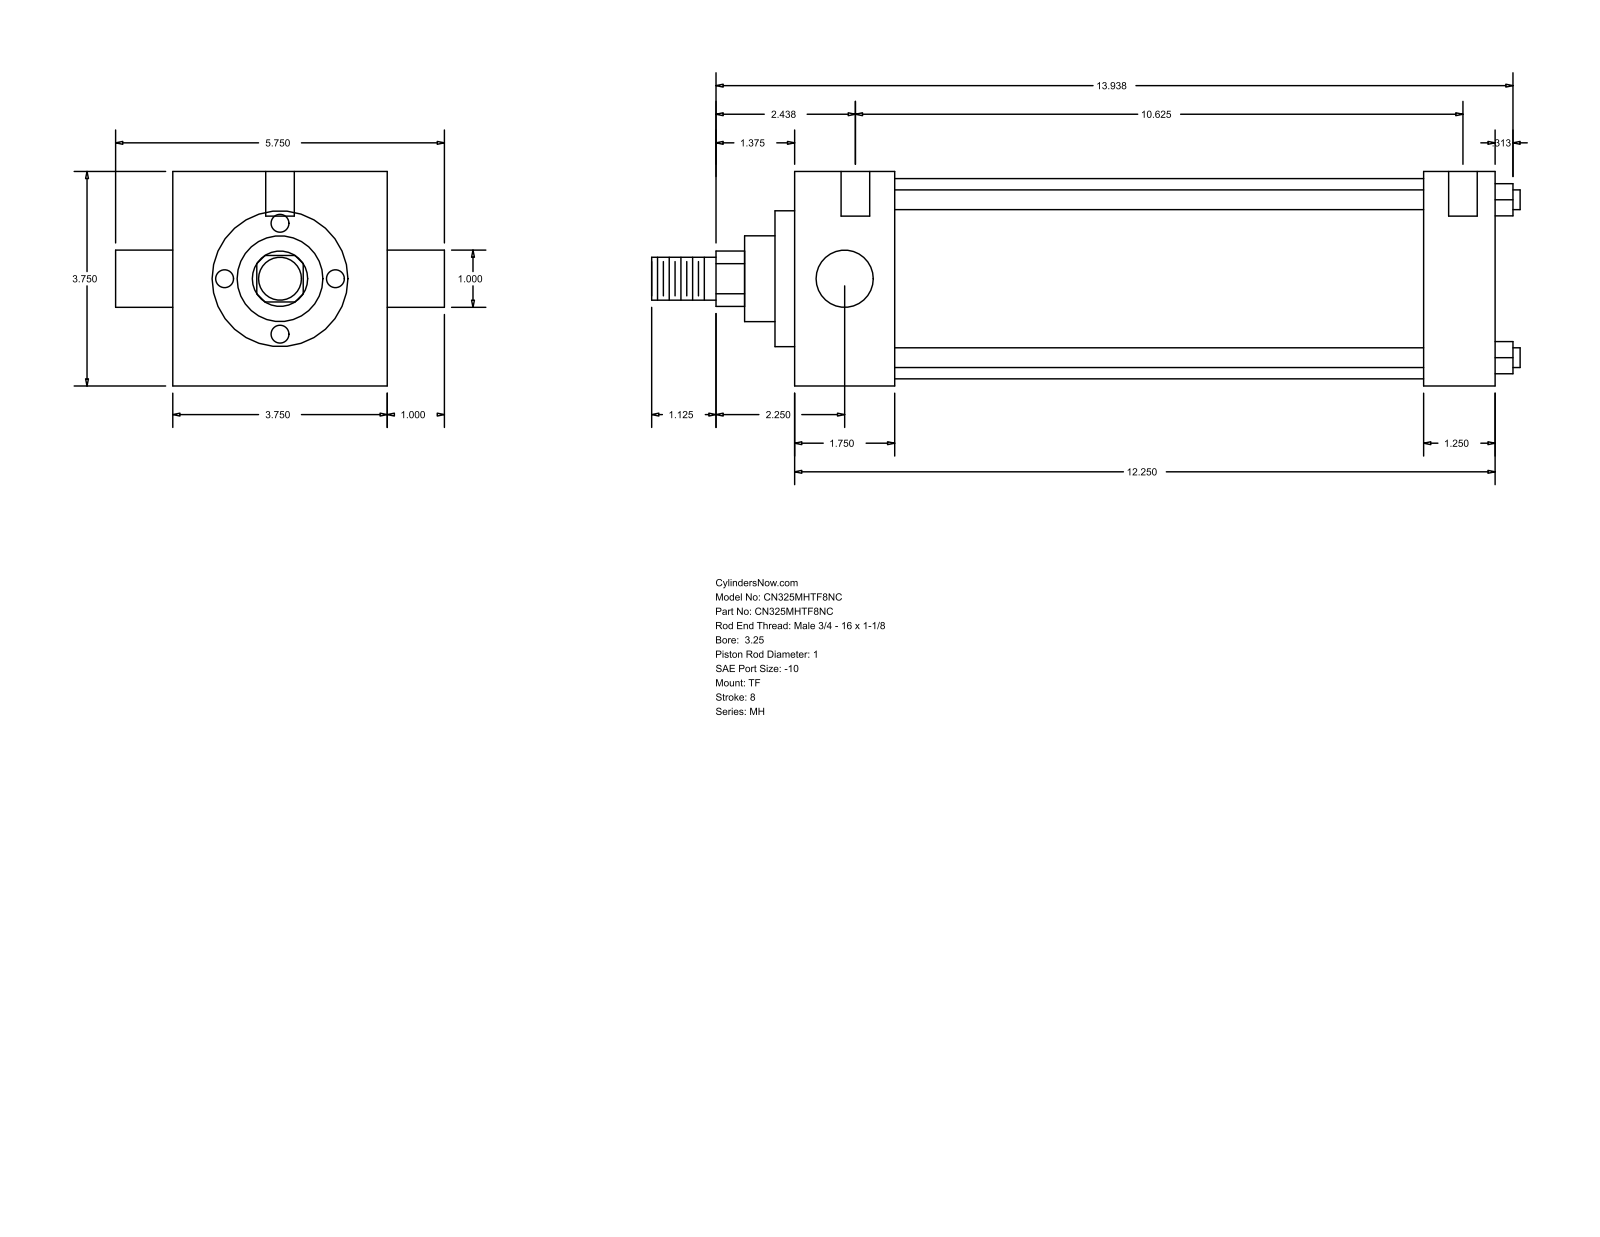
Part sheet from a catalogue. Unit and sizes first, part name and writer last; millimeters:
Units: millimetres
Overall size (bounding box): 385.76 × 146.05 × 95.25
Round holes (diameter × count): ⌀5.56 ×3, ⌀12.7 ×2
Round bosses / shafts (diameter × count): ⌀8.76 ×4, ⌀25.4 ×2, ⌀88.9 ×1, ⌀60.33 ×1, ⌀38.1 ×1, ⌀19.05 ×1
Partial cylindrical surfaces — rounded edges, fillets, slot ends (radius × count): R12.29 ×1
Main face-to-face distances: 95.24, 311.15, 44.46, 279.4, 234.94, 266.69, 31.75, 8.73, 53.19, 288.13
Hole centre spacings: 1.58, 4.76, 269.88, 271.46, 274.64, 276.22
Bodies: 0 solids, 86 faces (61 planar, 25 cylindrical, 0 other)
Part name (STEP PRODUCT): MH_TF__0325_1
STEP written by: GSSL Pune (CONFIG_CONTROL_DESIGN)
